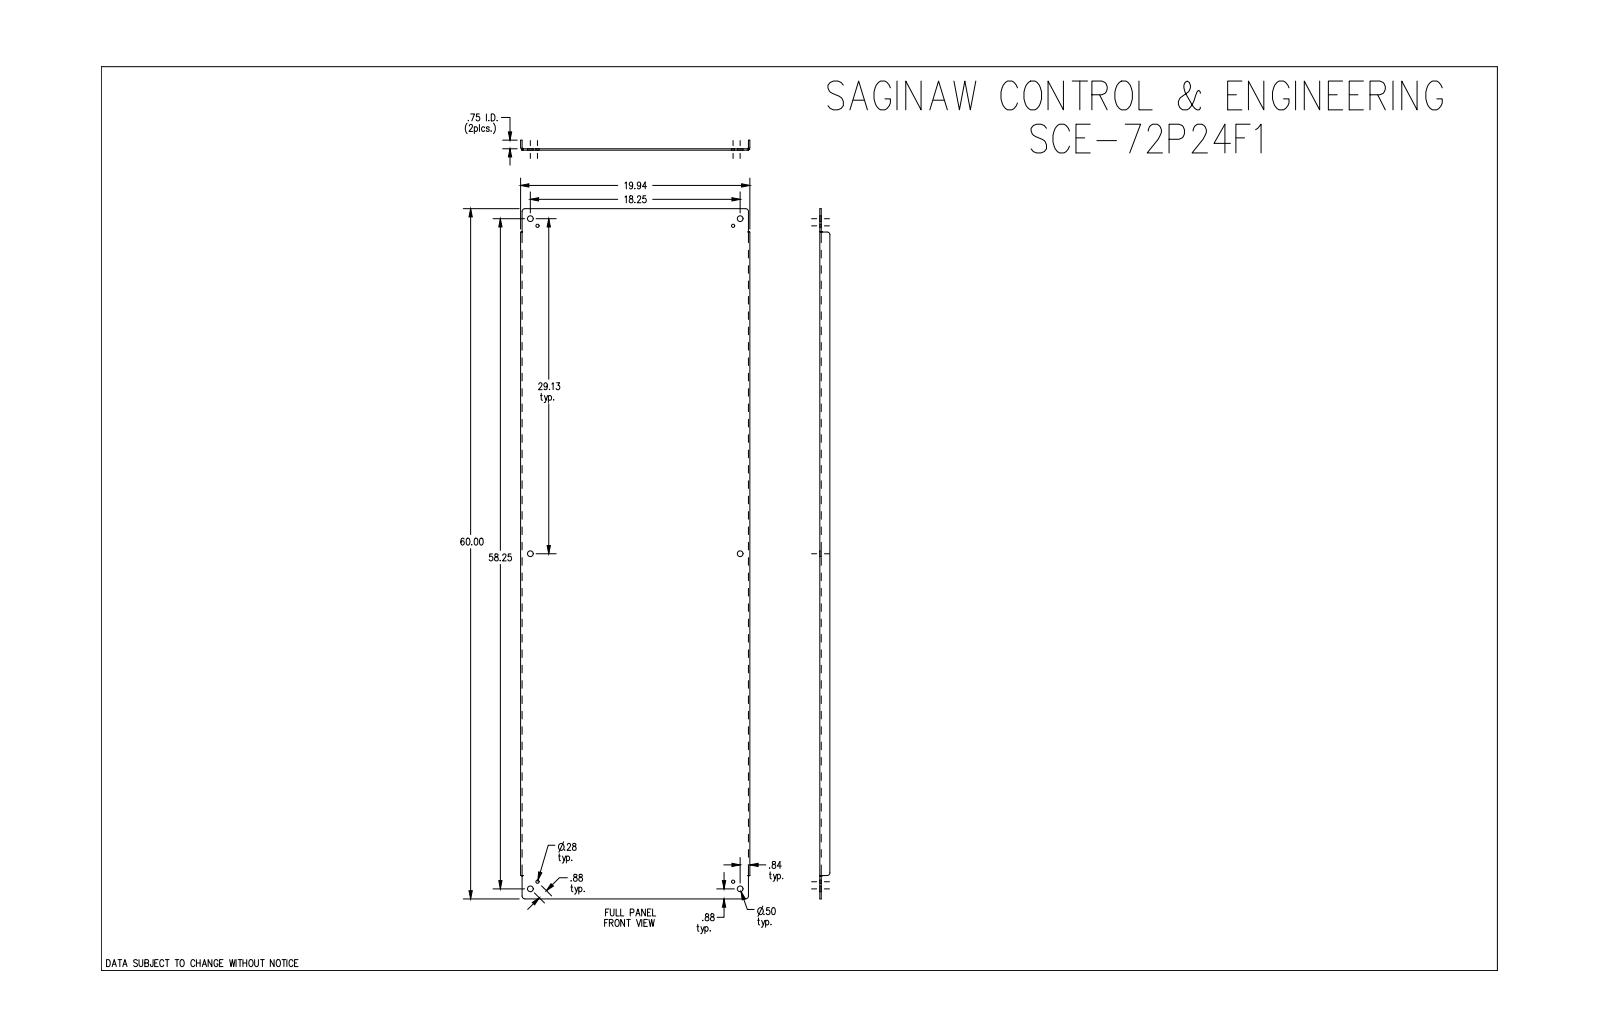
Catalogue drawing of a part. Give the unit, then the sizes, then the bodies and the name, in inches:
Units: inches
Overall size (bounding box): 60 × 19.938 × 0.875
Round holes (diameter × count): ⌀0.5 ×6, ⌀0.281 ×4
Partial cylindrical surfaces — rounded edges, fillets, slot ends (radius × count): R0.25 ×6, R0.112 ×2, R0.237 ×2
Main face-to-face distances: 0.125, 0.125, 19.813, 19.687, 19.938, 0.75, 0.875, 60, 2.031, 57.969
Hole centre spacings: 0.875, 17.642, 28.513, 29.125, 33.518, 34.37, 57.634, 60.268
Volume: 158.7 in³ · Surface area: 2 560 in²
Bodies: 1 solid, 52 faces (18 planar, 22 cylindrical, 12 other)
Part name (STEP PRODUCT): SCE-72P24F1
STEP written by: SolidWorks 2019 (CONFIG_CONTROL_DESIGN)
